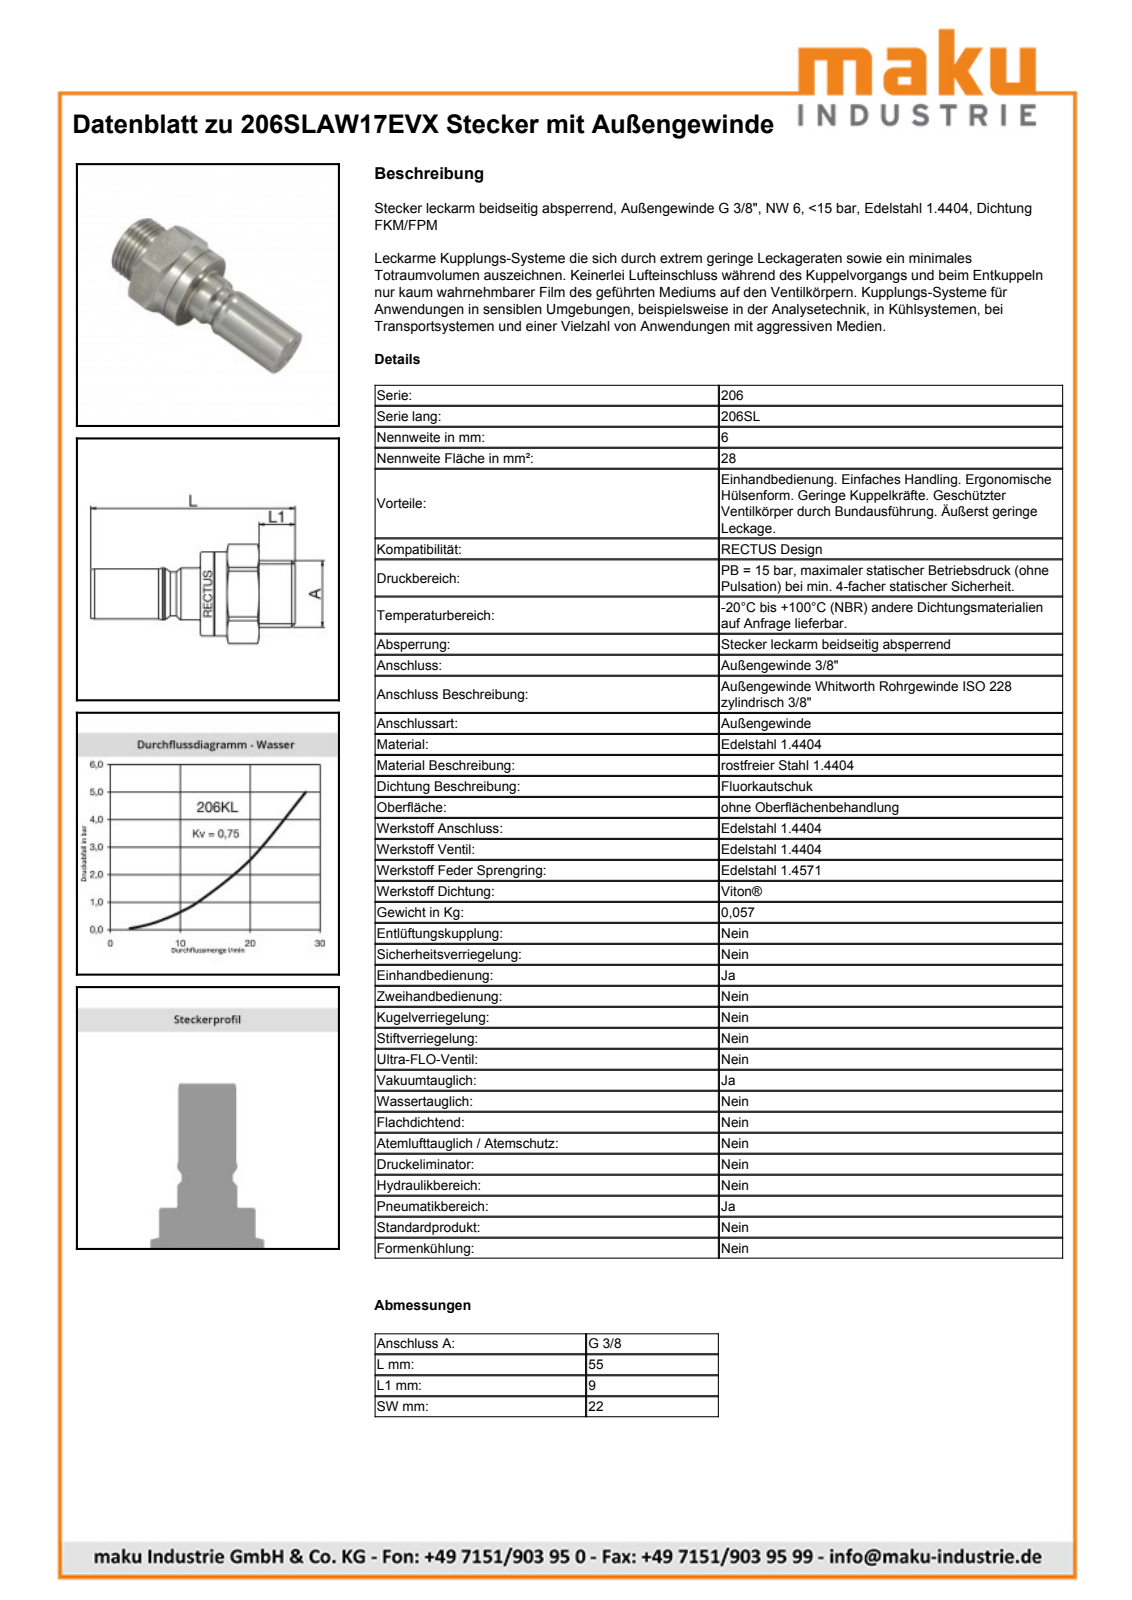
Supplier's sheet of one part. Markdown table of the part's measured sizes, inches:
| quantity | value |
| --- | --- |
| part name | D108139 |
| STEP written by | Autodesk Inventor 2013 (AUTOMOTIVE_DESIGN) |
| units | inches |
| bodies | 1 solid, 70 faces (16 planar, 21 cylindrical, 33 other) |
| overall size | 2.014 × 0.974 × 0.914 |
| volume | 0.644 in³ |
| surface area | 7.789 in² |
| round holes (diameter × count) | 0.402 × 1, 0.569 × 1, 0.669 × 1, 0.776 × 1 |
| round bosses / shafts (diameter × count) | 0.827 × 1, 0.656 × 1, 0.656 × 1, 0.553 × 1, 0.51 × 1, 0.492 × 1, 0.433 × 1, 0.384 × 1 |
| partial cylindrical surfaces (radius × count) | 0.488 × 1 |
| main face-to-face distances | 0.866, 0.354, 0.931, 0.577, 1.083, 1.659, 2.014, 1.498, 0.415, 0.161 |
